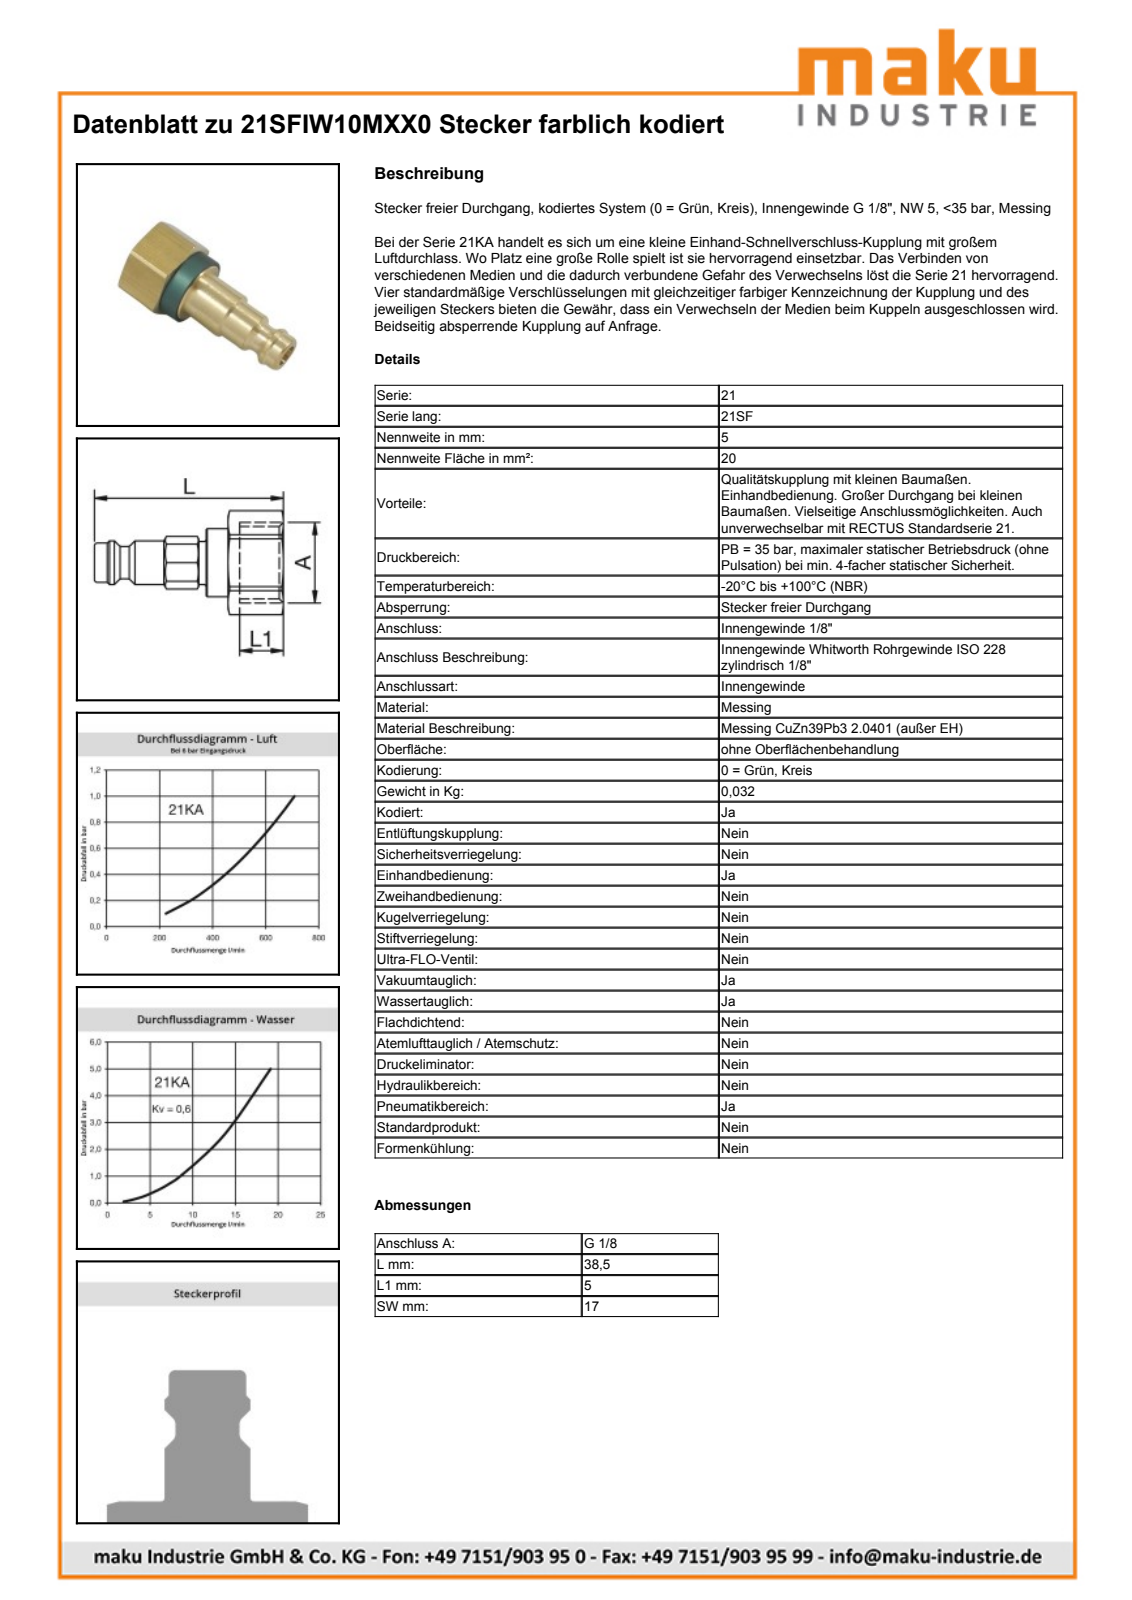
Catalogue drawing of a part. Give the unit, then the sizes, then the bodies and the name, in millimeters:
Units: millimetres
Overall size (bounding box): 43 × 15.5 × 15.5
Round holes (diameter × count): ⌀2.95 ×1, ⌀4.95 ×1, ⌀13.85 ×1, ⌀14.05 ×1
Round bosses / shafts (diameter × count): ⌀15.5 ×1, ⌀15 ×1, ⌀14 ×1, ⌀10.4 ×1, ⌀10 ×1, ⌀9 ×1, ⌀8.6 ×1, ⌀8.4 ×1
Main face-to-face distances: 6.25, 6.15, 12.4, 8.2, 2.05, 4.2, 7.9, 1.75, 4.5, 35.9
Volume: 2 551 mm³ · Surface area: 2 644 mm²
Bodies: 2 solids, 45 faces (9 planar, 17 cylindrical, 19 other)
Part name (STEP PRODUCT): D113141; D113142; D113125
STEP written by: Autodesk Inventor 2013 (AUTOMOTIVE_DESIGN)
